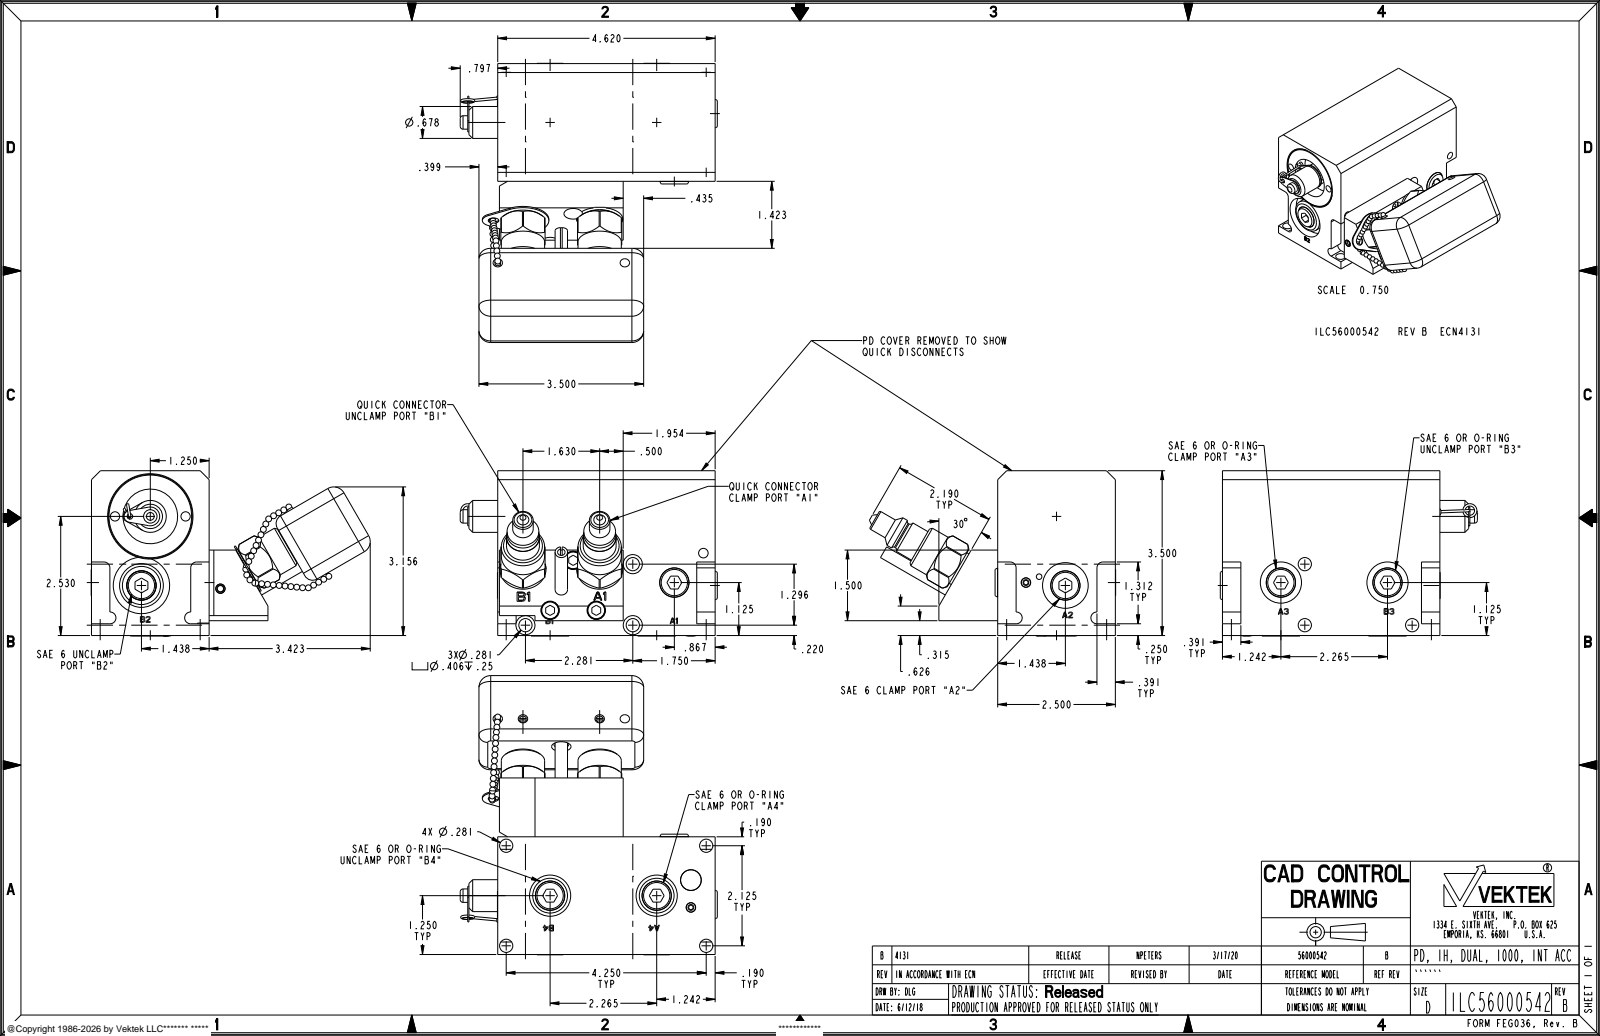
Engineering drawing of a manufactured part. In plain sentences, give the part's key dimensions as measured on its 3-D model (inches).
The part is named "ILC56000542_PD; ILC56000542_COVER; ILC56000542". Its 3-D file was written by "PRO/ENGINEER BY PARAMETRIC TECHNOLOGY CORPORATION, 2013320 (AUTOMOTIVE_DESIGN)". It is 3 solids with 1400 faces: 774 planar, 232 cylindrical and 394 other. Overall it measures 5.929 by 5.463 by 3.515 inches. Its volume is 43.74 cubic inches and its surface area 170.3 square inches. Round holes: 7 of diameter 0.281, 5 of diameter 0.875, 3 of diameter 0.391, 3 of diameter 0.406, 2 of diameter 0.118, 2 of diameter 0.123, 2 of diameter 0.197, 2 of diameter 0.2, 2 of diameter 0.201, 2 of diameter 0.201, 2 of diameter 0.203, 2 of diameter 0.979. Round bosses or shafts: 4 of diameter 0.555, 4 of diameter 0.48, 3 of diameter 0.375, 2 of diameter 0.92, 2 of diameter 0.75, 2 of diameter 0.699, 2 of diameter 0.675, 2 of diameter 0.585. Partial cylindrical surfaces (rounded edges, fillets, slot ends): 8 of radius 0.25, 6 of radius 0.125, 4 of radius 0.187, 2 of radius 0.536, 1 of radius 0.108, 1 of radius 0.166, 1 of radius 0.2, 1 of radius 0.237. The main face-to-face distances are 2.5, 3.5, 0.391, 4.62, 1.55, 4.229, 1.6, 0.435, 3.065, 0.315. The hole center spacings are 0.535, 0.75, 0.956, 1.493, 1.63, 2.125, 2.165, 2.265.
